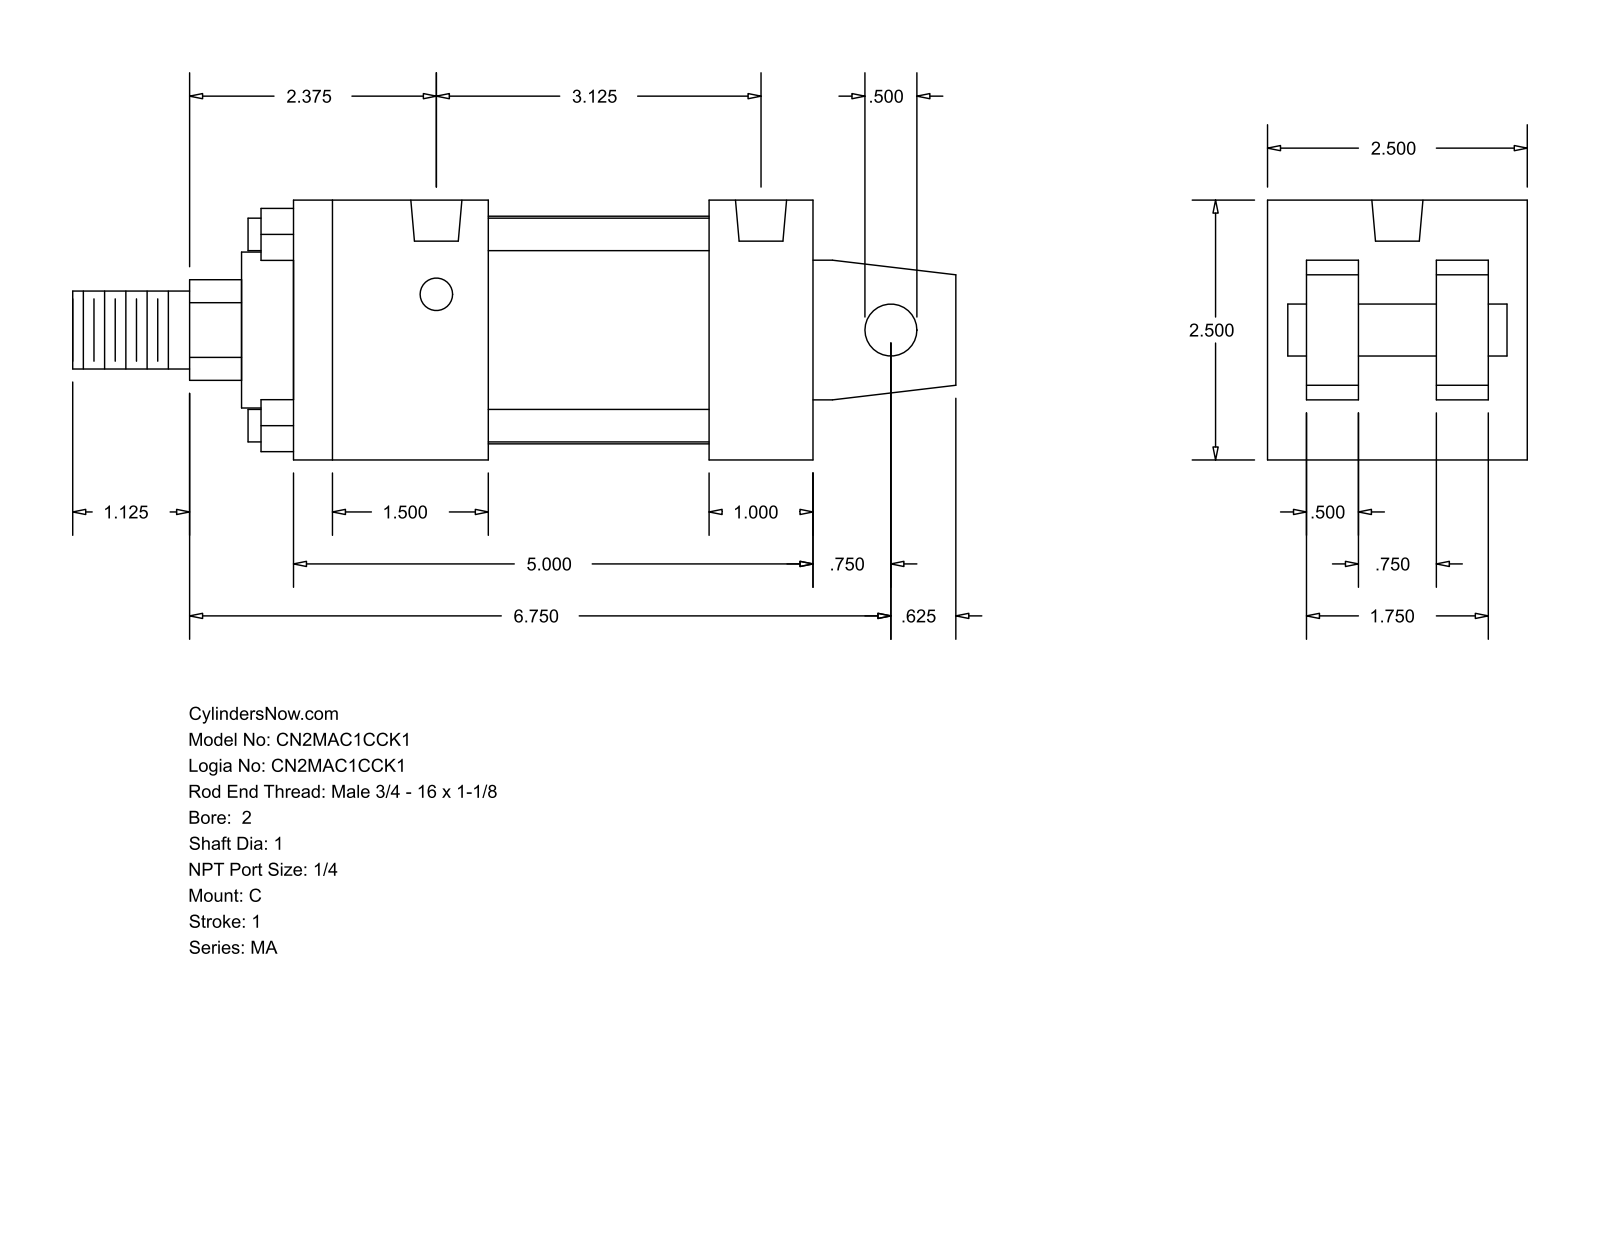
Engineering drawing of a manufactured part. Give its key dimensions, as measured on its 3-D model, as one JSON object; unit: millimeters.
{"part_name": "MA_C__0200_1", "step_written_by": "GSSL Pune (CONFIG_CONTROL_DESIGN)", "units": "millimeters", "bodies": {"solids": 0, "faces": 103, "planar": 76, "cylindrical": 27, "other": 0}, "overall_size": [215.9, 63.5, 63.5], "round_holes": [[7.94, 4], [12.49, 2]], "round_bosses_or_shafts": [[7.94, 4], [55.63, 1], [38.1, 1], [25.4, 1], [19.05, 1], [12.7, 1]], "partial_cylinders_radius": [[12.29, 1]], "face_to_face_distances": [63.5, 12.7, 127, 22.22, 41.28, 9.52, 53.98, 31.76, 53.97, 101.6], "hole_center_spacings": [79.37]}
